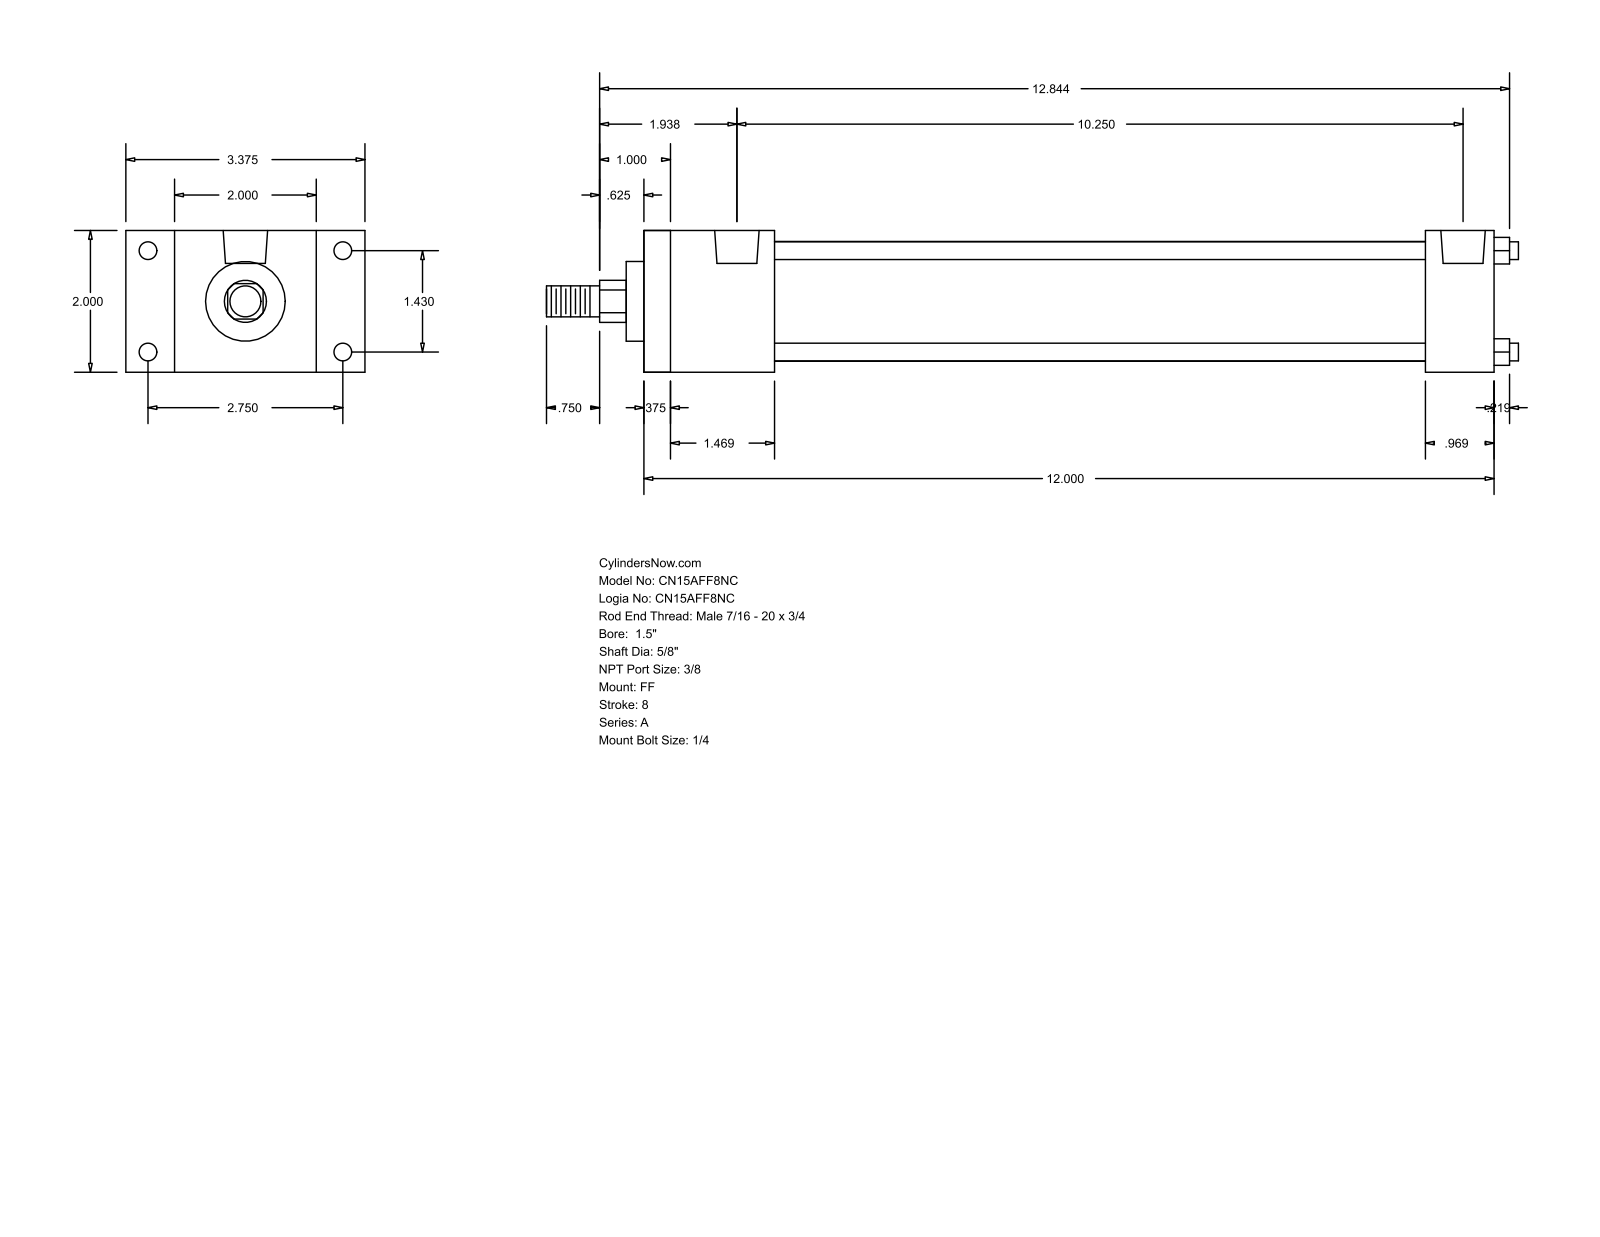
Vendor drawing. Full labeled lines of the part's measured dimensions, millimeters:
Part name (STEP PRODUCT): A_FF__0150_0.625
STEP written by: GSSL Pune (CONFIG_CONTROL_DESIGN)
Units: millimetres
Bodies: 0 solids, 92 faces (64 planar, 28 cylindrical, 0 other)
Overall size (bounding box): 348.46 × 85.72 × 50.8
Round holes (diameter × count): ⌀5.56 ×4, ⌀6.35 ×4, ⌀15.93 ×2
Round bosses / shafts (diameter × count): ⌀6.35 ×4, ⌀42.93 ×1, ⌀28.57 ×1, ⌀15.88 ×1, ⌀11.11 ×1
Partial cylindrical surfaces — rounded edges, fillets, slot ends (radius × count): R7.54 ×1
Main face-to-face distances: 50.8, 304.8, 9.52, 295.28, 46.83, 280.19, 37.31, 270.67, 233.36, 257.97
Hole centre spacings: 3.97, 36.32, 69.84, 78.72, 252.41, 256.38, 260.35
